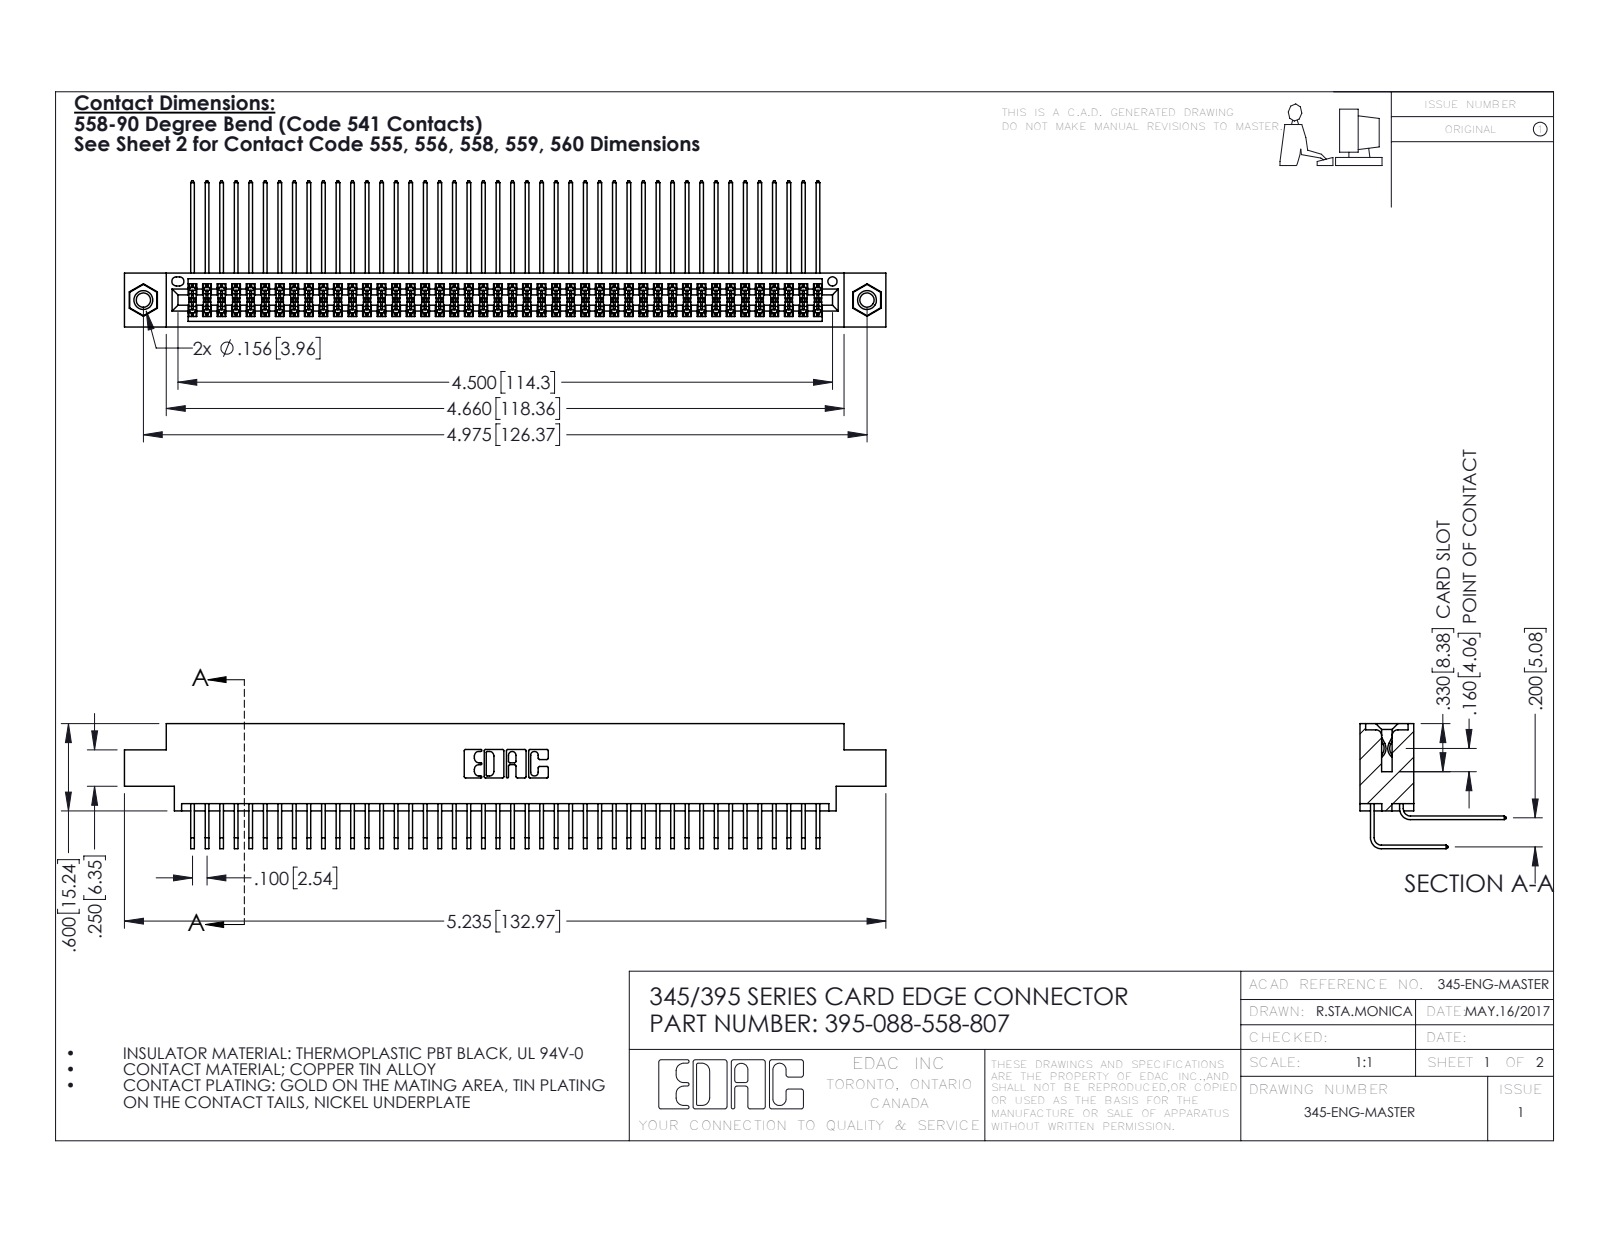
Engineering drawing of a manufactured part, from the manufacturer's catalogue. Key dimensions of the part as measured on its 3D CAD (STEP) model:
Part name (STEP PRODUCT): 345-292-001_558 559 Tail - 1; 345-250-001_345-250-005-103; 345-292-001_558 Tail - 2; 345 Part_0.170 Offset - 0.156 Dia-TI (+1 more)
STEP written by: SolidWorks 2016 (CONFIG_CONTROL_DESIGN)
Units: inches
Bodies: 91 solids, 4766 faces (3196 planar, 1554 cylindrical, 16 other)
Overall size (bounding box): 5.235 × 1.005 × 0.859
Volume: 0.813 in³ · Surface area: 34.53 in²
Round holes (diameter × count): ⌀0.098 ×2, ⌀0.125 ×2, ⌀0.156 ×2, ⌀0.064 ×1
Round bosses / shafts (diameter × count): ⌀0.155 ×2
Partial cylindrical surfaces — rounded edges, fillets, slot ends (radius × count): R0.006 ×133, R0.01 ×22, R0.007 ×6, R0.031 ×6, R0.026 ×3, R0.014 ×2, R0.019 ×2, R0.022 ×2
Main face-to-face distances: 0.072, 0.298, 0.2, 0.37, 0.098, 0.272, 0.025, 0.225, 0.175, 0.025
Hole centre spacings: 0.27, 4.739, 4.975
